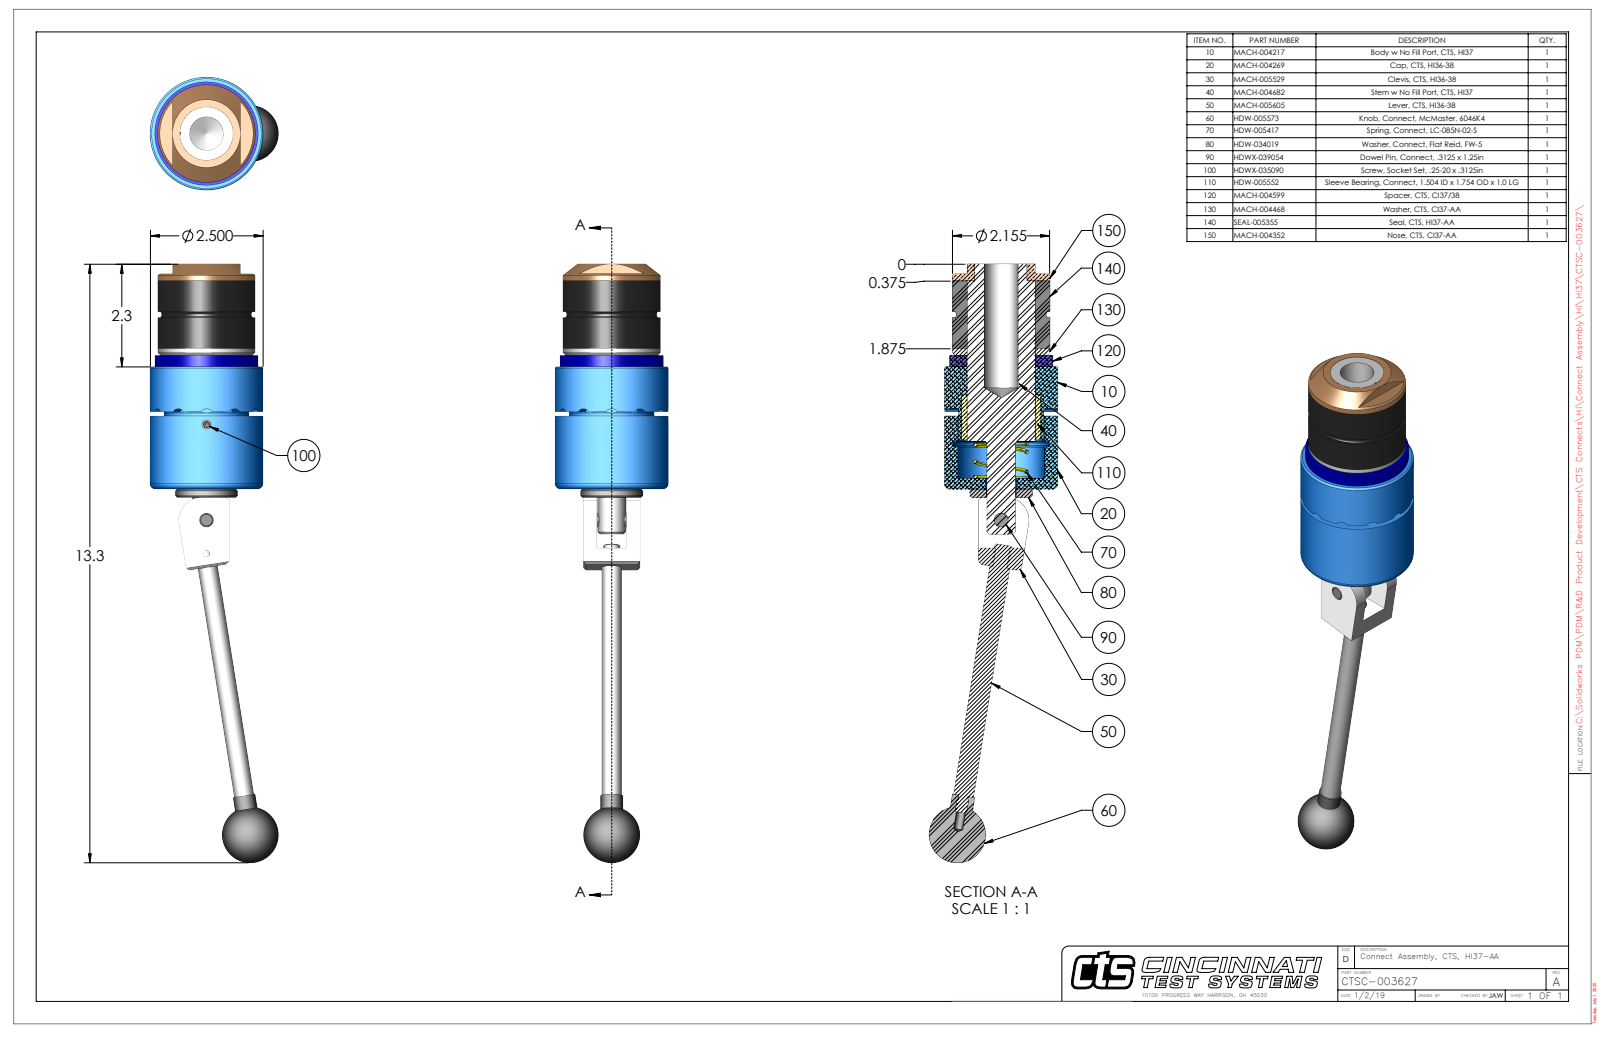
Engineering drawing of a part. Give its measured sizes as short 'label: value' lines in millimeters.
name: CTSC-003627
written by: SolidWorks 2023 (AUTOMOTIVE_DESIGN)
unit: mm
bodies: 10 solids, 350 faces (156 planar, 111 cylindrical, 83 other)
size: 337.2 × 72.2 × 63.5
volume: 384 300 mm³; area: 83 030 mm²
holes: 2× ⌀5.1, 1× ⌀3.8, 1× ⌀7.9, 1× ⌀8, 1× ⌀8, 1× ⌀16.7, 1× ⌀17.7, 1× ⌀19.1, 1× ⌀29.8, 1× ⌀38, 1× ⌀38.1, 1× ⌀38.4
bosses: 1× ⌀63.5, 1× ⌀57.9, 1× ⌀54.7, 1× ⌀54.7, 1× ⌀47.6, 1× ⌀38.1, 1× ⌀38, 1× ⌀35.1
rounds: 12× R3, 2× R0.7, 1× R12.7, 1× R30.1
face distances: 48.3, 68.9, 117.2, 6.4, 38.1, 75.3, 42, 79.1, 10.2, 3.9
hole spacings: 18.8, 53.8, 72.6
